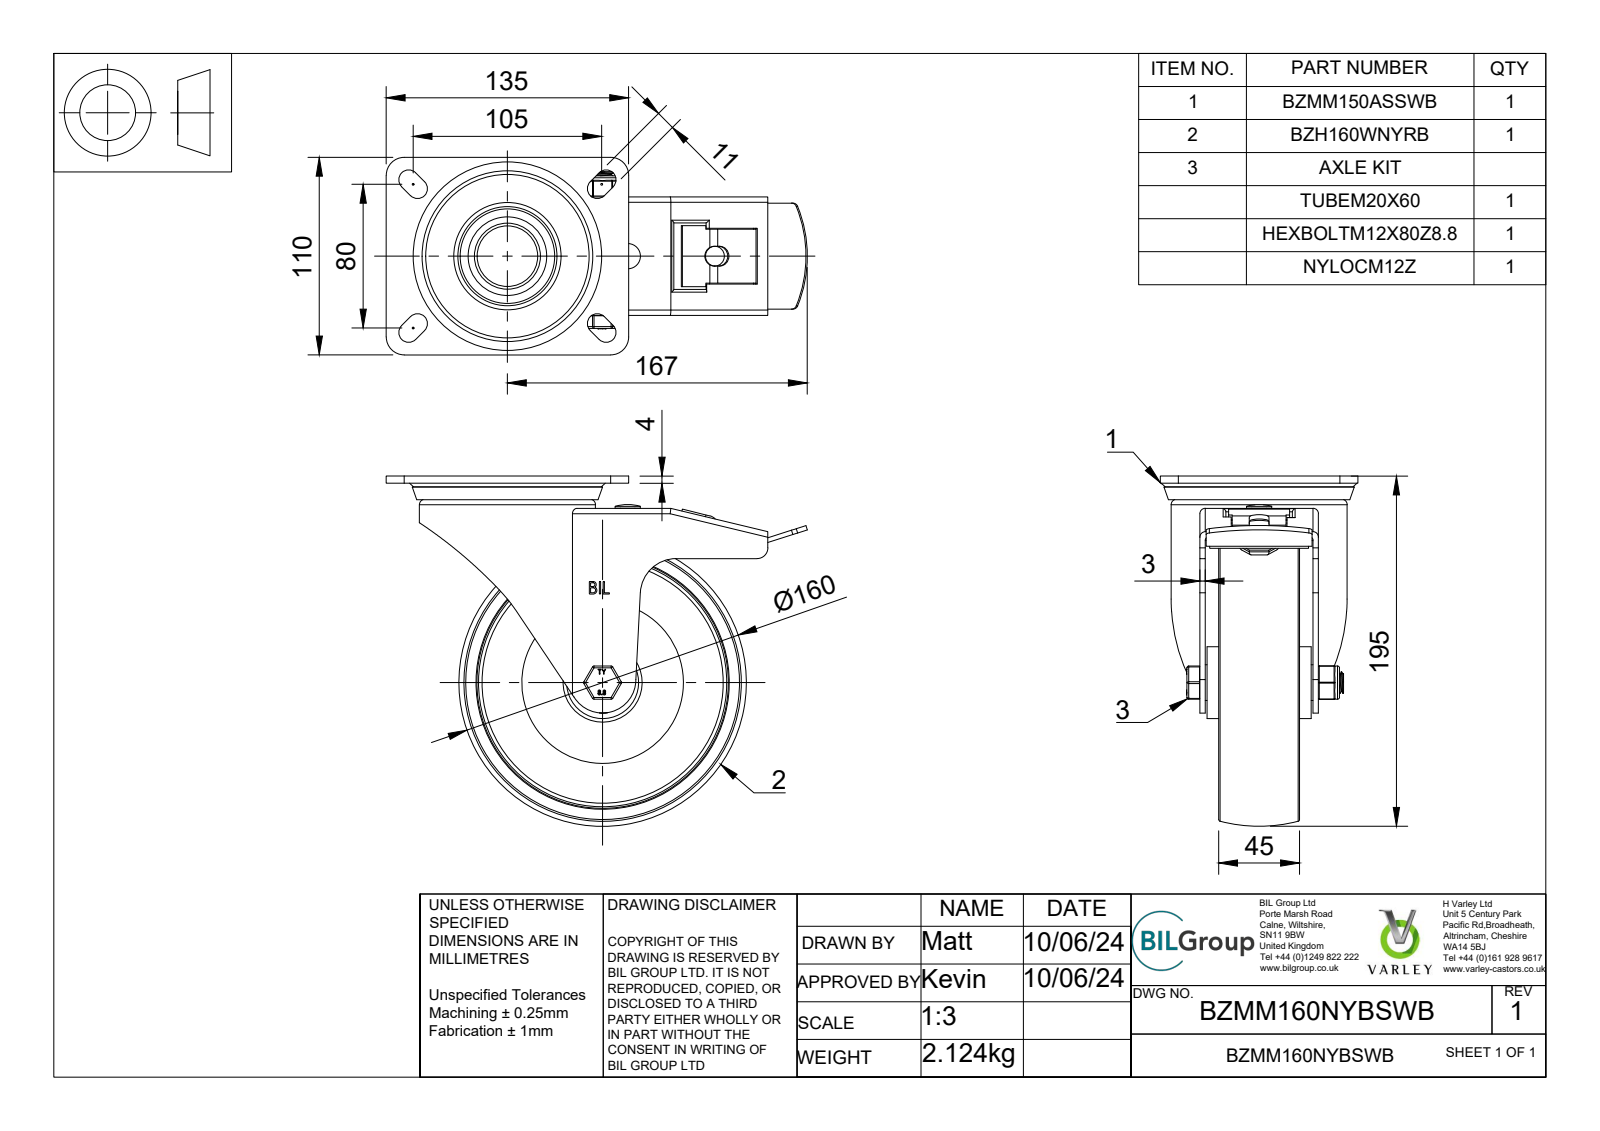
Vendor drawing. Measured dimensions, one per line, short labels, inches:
name: BZMM160NYBSWB v3; BZMM150ASSWB v1; ZINC PLATED, PRESSED STEEL TOP PLATE; ZINC PLATED, PRESSED STEEL TOP PLATE Geometry (+7 more)
written by: Autodesk Translation Framework v13.14.0.145 (AUTOMOTIVE_DESIGN)
unit: in
bodies: 63 solids, 642 faces (308 planar, 189 cylindrical, 145 other)
size: 9.232 × 7.677 × 4.331
volume: 38.3 in³; area: 402.5 in²
holes: 1× ⌀0.315, 1× ⌀0.433, 1× ⌀0.472, 1× ⌀0.48, 1× ⌀0.492, 1× ⌀0.551, 1× ⌀0.787, 1× ⌀0.795, 1× ⌀1.329, 1× ⌀1.565, 1× ⌀3.622
bosses: 8× ⌀0.295, 1× ⌀3.858, 1× ⌀3.071, 1× ⌀1.969, 1× ⌀1.575, 1× ⌀1.339, 1× ⌀0.783, 1× ⌀0.728
rounds: 18× R0.02, 12× R0.039, 10× R0.059, 10× R0.217, 6× R0.01, 6× R0.098, 6× R0.118, 4× R0.394
face distances: 0.118, 0.354, 0.157, 0.197, 0.984, 0.472, 1.102, 1.496, 2.48, 1.378
hole spacings: 2.638
